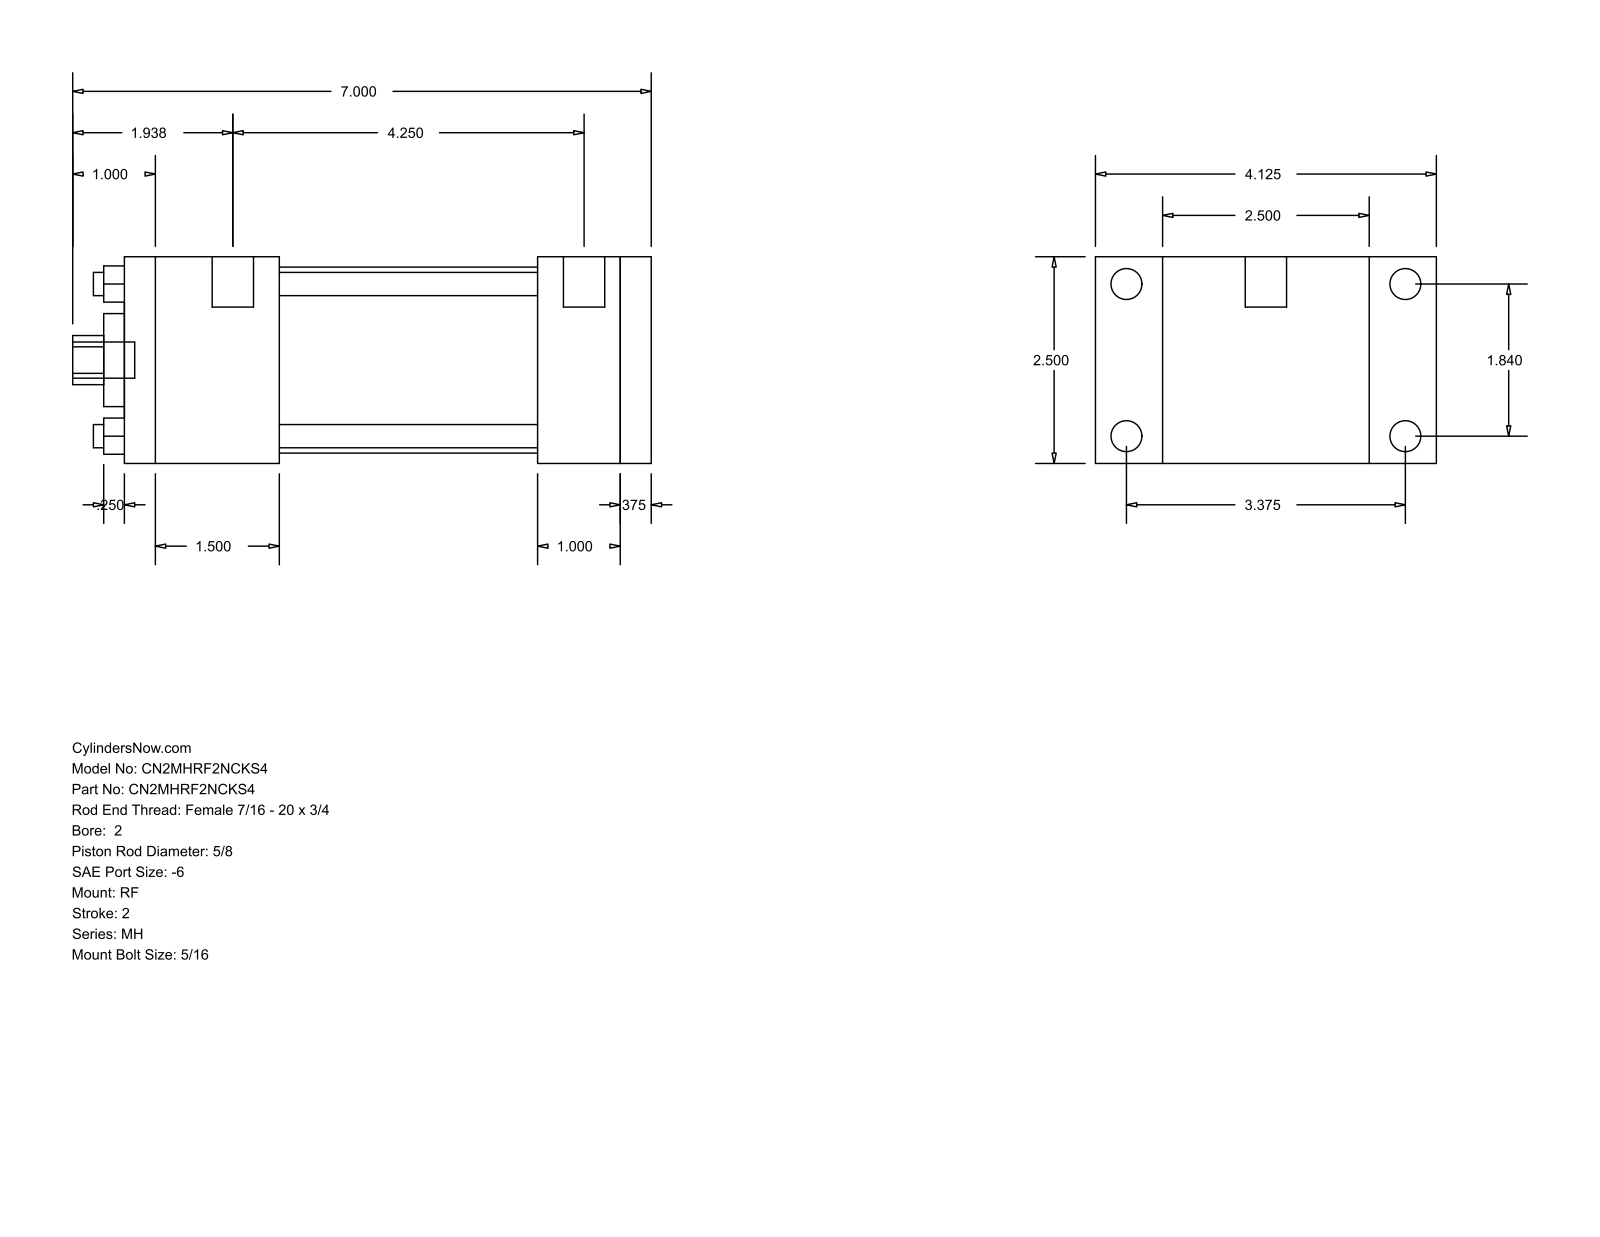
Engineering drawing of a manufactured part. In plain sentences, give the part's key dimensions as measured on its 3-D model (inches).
The part is named "MH_RF__0200_0.625". Its 3-D file was written by "GSSL Pune (CONFIG_CONTROL_DESIGN)". It is 0 solids with 92 faces: 64 planar, 28 cylindrical and 0 other. Overall it measures 7 by 4.125 by 2.5 inches. Round holes: 4 of diameter 0.281, 1 of diameter 0.625, 1 of diameter 1.125, 1 of diameter 2.25. Round bosses or shafts: 4 of diameter 0.375, 4 of diameter 0.219, 2 of diameter 0.5, 1 of diameter 0.437. Partial cylindrical surfaces (rounded edges, fillets, slot ends): 1 of radius 0.297. The main face-to-face distances are 2.5, 6.375, 0.375, 6, 4.125, 1, 1.875, 5, 3.125, 4.5. The hole center spacings are 1.301, 1.84, 2.602.
